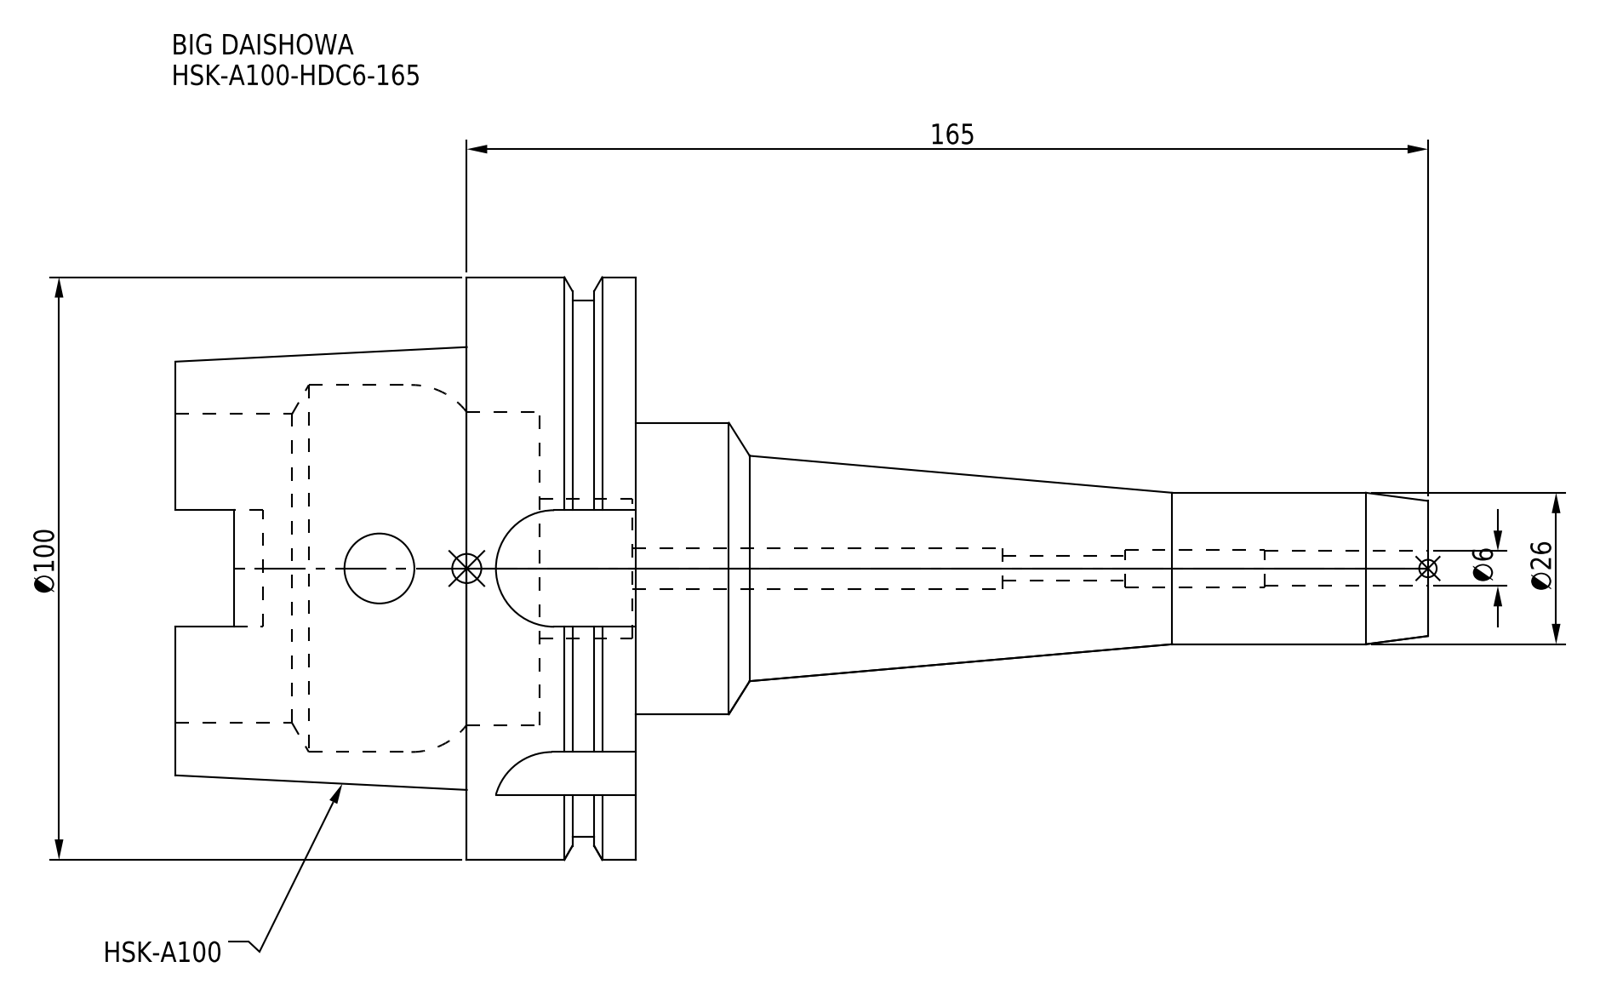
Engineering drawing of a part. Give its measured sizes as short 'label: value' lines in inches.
name: HSK-A100-HDC6-165
written by: CREO PARAMETRIC BY PTC INC, 2016380 (AUTOMOTIVE_DESIGN)
unit: in
bodies: 1 solid, 97 faces (35 planar, 42 cylindrical, 20 other)
size: 8.465 × 3.937 × 3.937
volume: 22.53 in³; area: 101.6 in²
holes: 1× ⌀0.165, 1× ⌀0.236, 1× ⌀0.256, 1× ⌀0.276, 1× ⌀0.472, 1× ⌀0.945, 1× ⌀2.087, 1× ⌀2.118, 1× ⌀2.48
bosses: 1× ⌀3.937, 1× ⌀3.622, 1× ⌀1.969, 1× ⌀1.024
rounds: 4× R0.192, 4× R0.394
face distances: 1.142, 0.652, 0.49, 3.11, 2.459, 1.969, 3.465, 0.022, 0.63, 1.12
